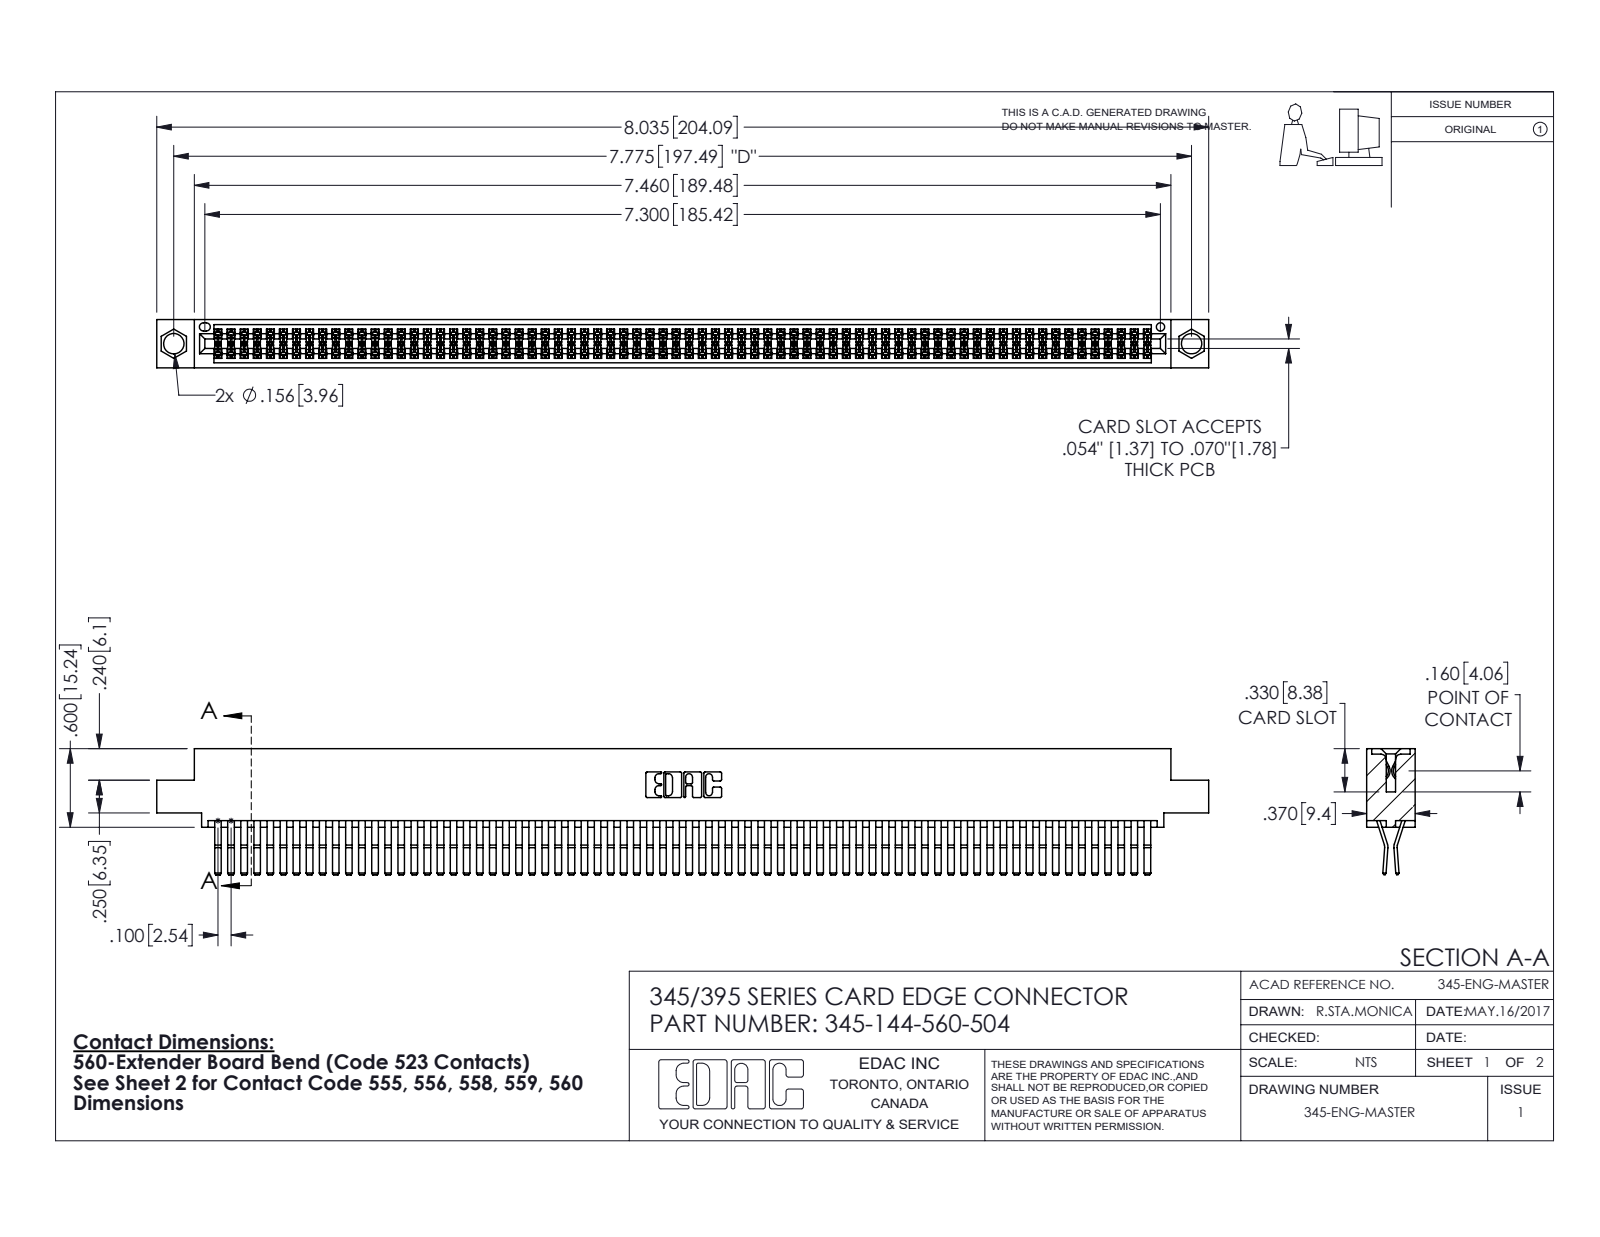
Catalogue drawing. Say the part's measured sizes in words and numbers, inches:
The part is named "345-292-001_560 Tail; 345 Part_0.110 Offset - 0.156 Dia-TI; 345-144-560-504". Its 3-D file was written by "SolidWorks 2020 (CONFIG_CONTROL_DESIGN)". It is 145 solids with 7632 faces: 4850 planar, 2782 cylindrical and 0 other. Overall it measures 8.035 by 0.962 by 0.37 inches. Its volume is 1.273 cubic inches and its surface area 52.39 square inches. Round holes: 2 of diameter 0.156, 1 of diameter 0.064. Partial cylindrical surfaces (rounded edges, fillets, slot ends): 216 of radius 0.006, 22 of radius 0.01, 6 of radius 0.007, 6 of radius 0.031, 3 of radius 0.026, 2 of radius 0.01, 2 of radius 0.014, 2 of radius 0.019. The main face-to-face distances are 0.025, 0.298, 0.072, 0.37, 0.2, 0.098, 0.272, 0.225, 0.175, 0.149. The hole center spacings are 0.27, 7.539, 7.775.
